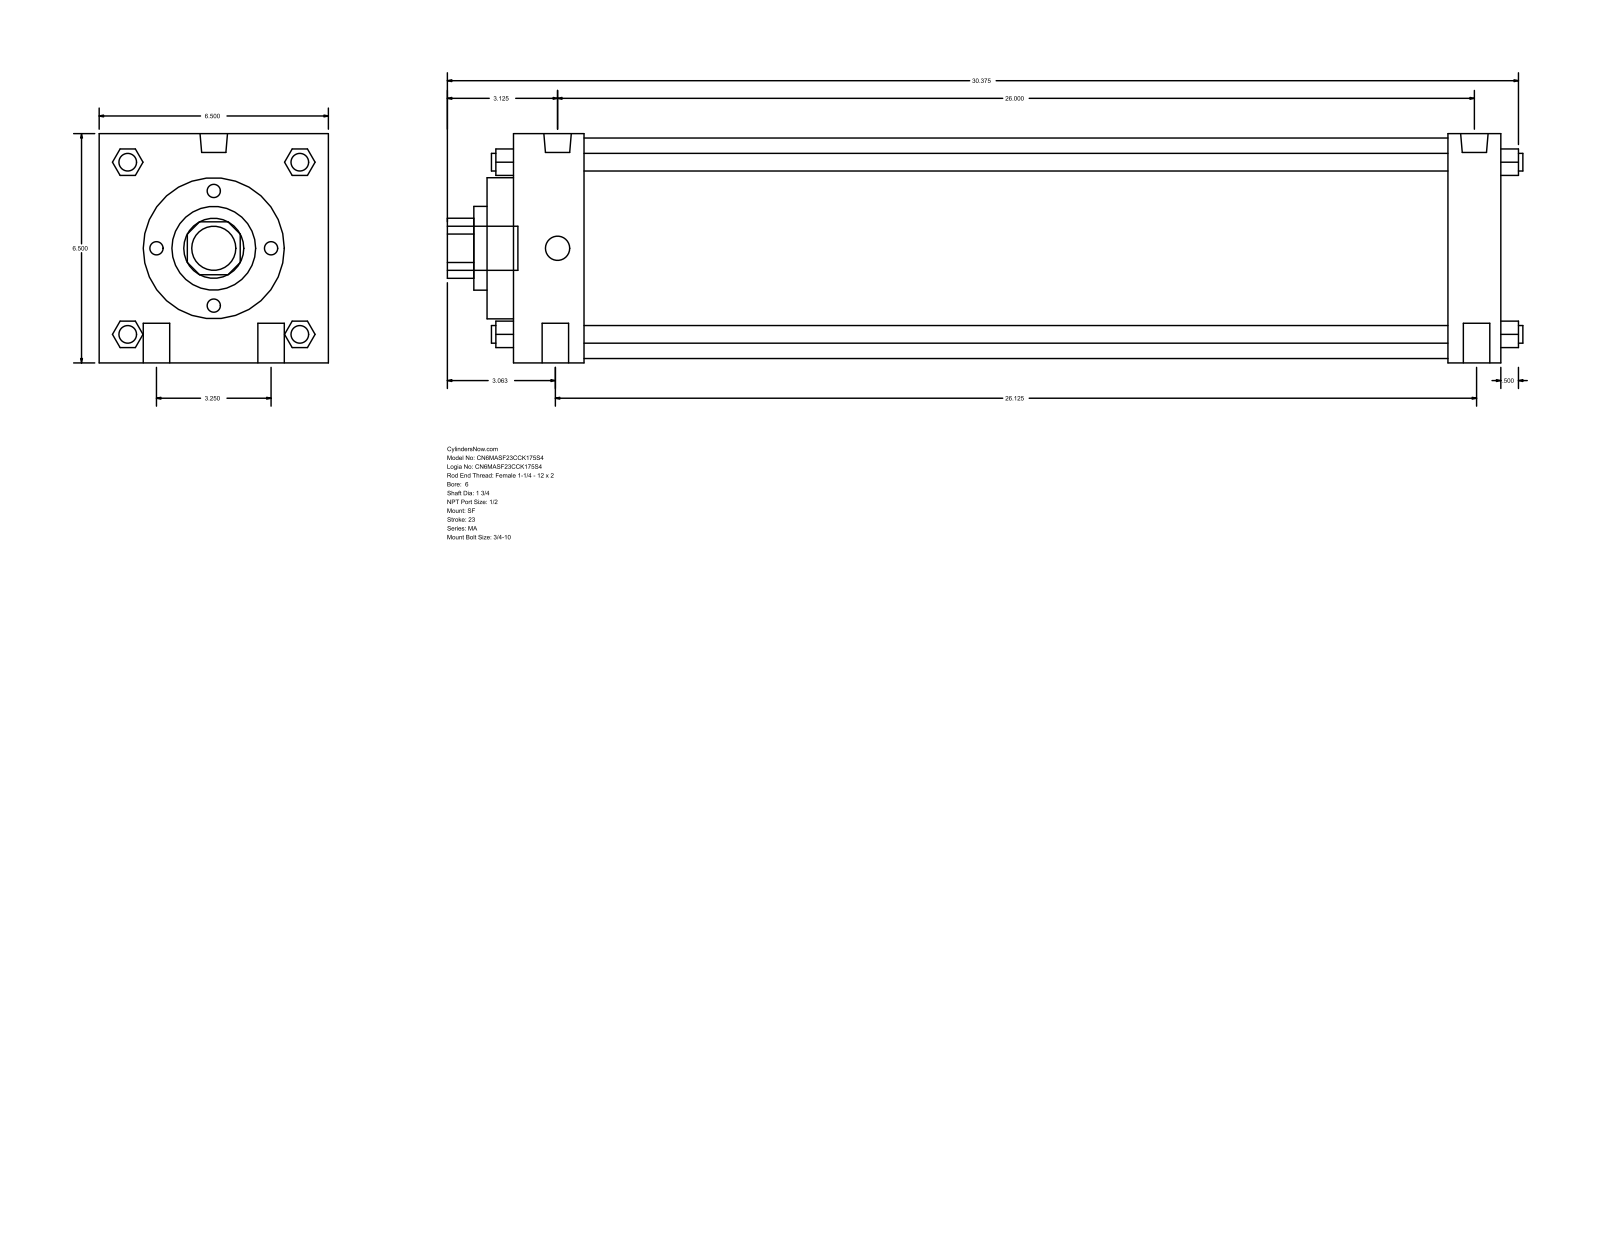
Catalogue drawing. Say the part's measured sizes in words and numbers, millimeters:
The part is named "MA_SF__0600_1.75". Its 3-D file was written by "GSSL Pune (CONFIG_CONTROL_DESIGN)". It is 0 solids with 126 faces: 95 planar, 31 cylindrical and 0 other. Overall it measures 774.7 by 165.1 by 165.1 millimeters. Round holes: 1 of diameter 44.45, 1 of diameter 60.33, 1 of diameter 101.6, 1 of diameter 158.75. Round bosses or shafts: 4 of diameter 19.05, 4 of diameter 12.7, 2 of diameter 19.77, 2 of diameter 17.46, 1 of diameter 31.75. Partial cylindrical surfaces (rounded edges, fillets, slot ends): 1 of radius 21.63. The main face-to-face distances are 165.1, 711.21, 19.05, 50.8, 38.1, 673.11, 622.31, 660.41, 69.85, 692.16.
